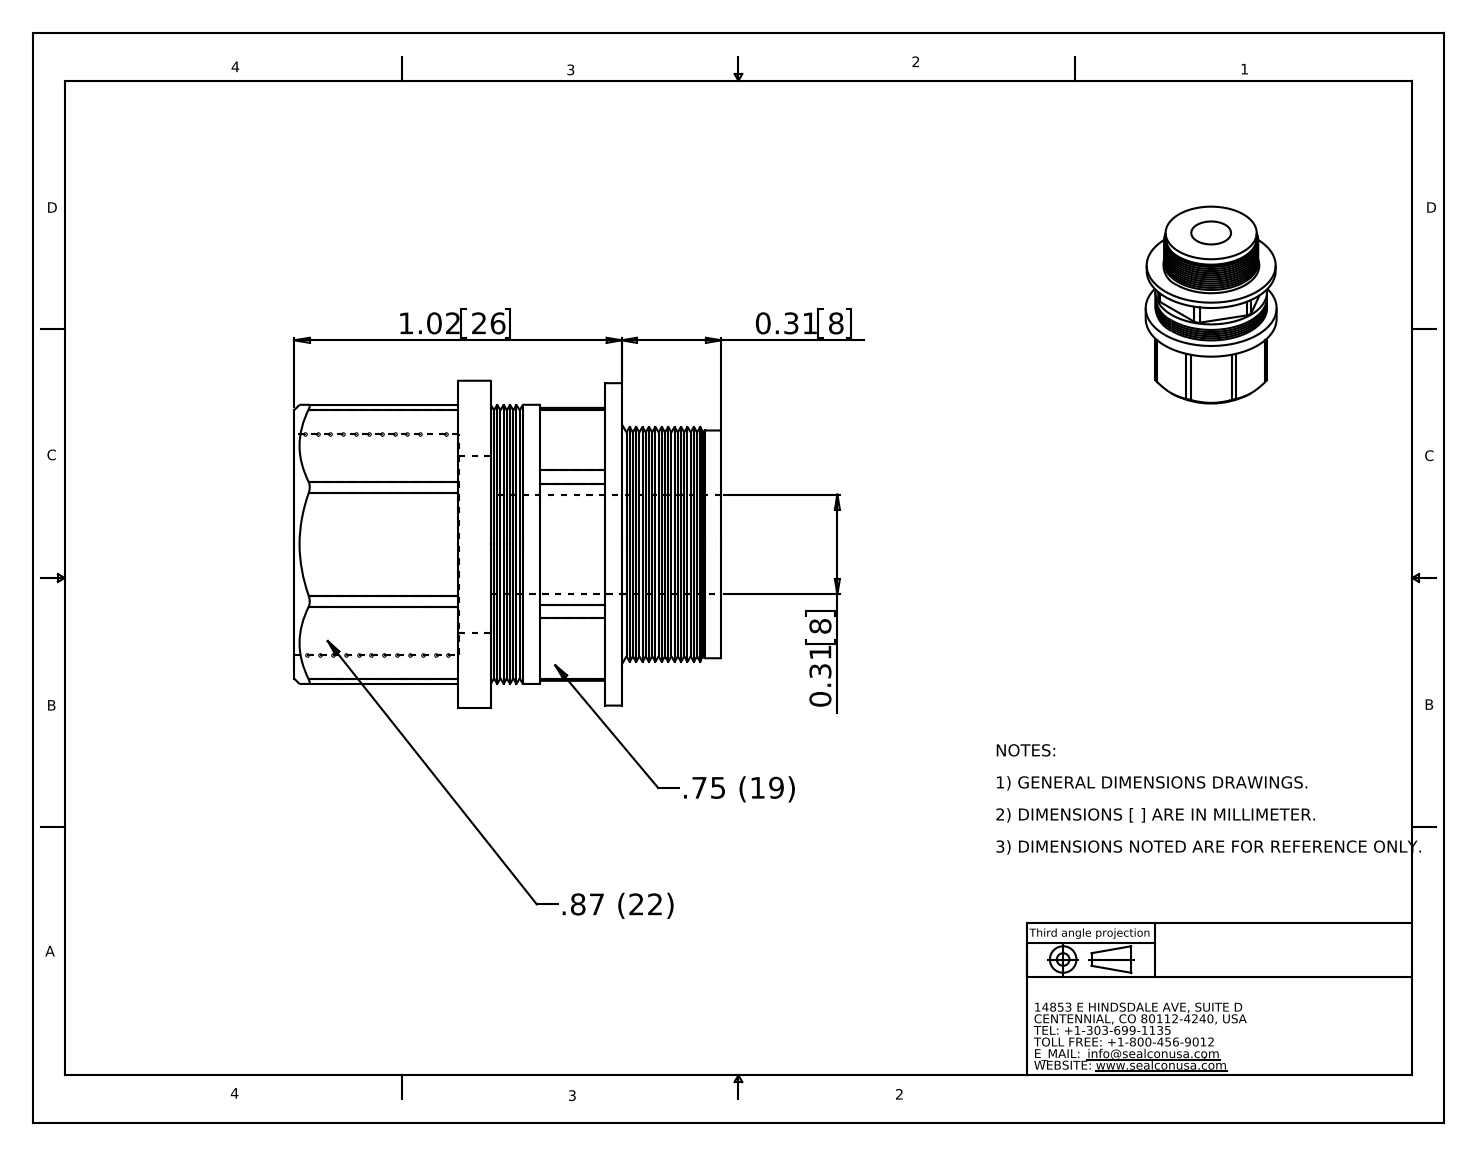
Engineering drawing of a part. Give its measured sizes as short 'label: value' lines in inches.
name: ST07AA-BK
written by: SolidWorks 2008 (CONFIG_CONTROL_DESIGN)
unit: in
bodies: 2 solids, 130 faces (24 planar, 30 cylindrical, 76 other)
size: 1.33 × 1.02 × 1.02
volume: 0.486 in³; area: 9.13 in²
holes: 1× ⌀0.31, 1× ⌀0.55, 1× ⌀0.687
bosses: 1× ⌀1.02, 1× ⌀1.005, 1× ⌀0.87, 1× ⌀0.71
rounds: 14× R0.05
face distances: 0.87, 0.408, 0.718, 0.31, 0.357, 0.051, 0.361, 0.255, 0.102, 0.459
